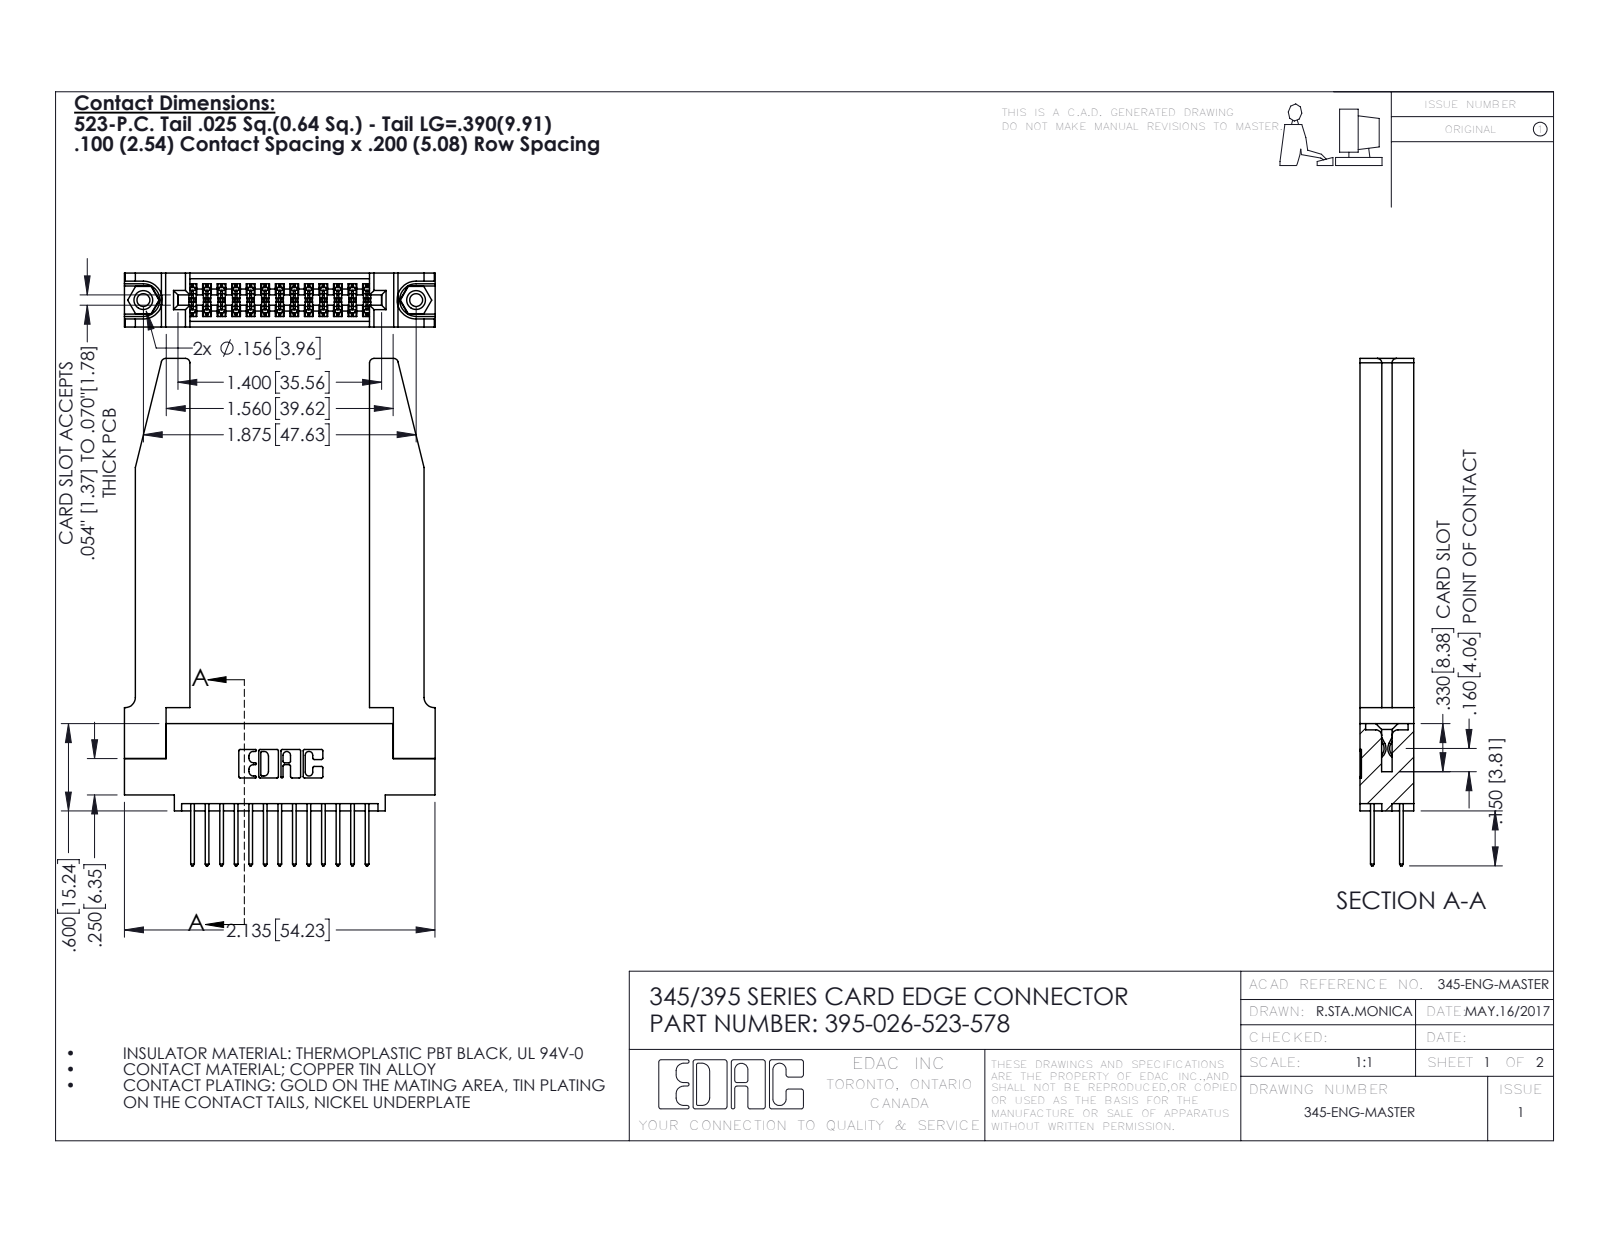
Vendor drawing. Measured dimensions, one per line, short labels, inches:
name: 395-026-523-578; 345 Part_0.110 Offset - 0.156 Dia-TH; 345-220-078_345-220-078; 345-250-001_345-250-001-102 (+1 more)
written by: SolidWorks 2016 (CONFIG_CONTROL_DESIGN)
unit: in
bodies: 31 solids, 1664 faces (1084 planar, 528 cylindrical, 52 other)
size: 3.487 × 2.136 × 0.37
volume: 0.778 in³; area: 21.66 in²
holes: 2× ⌀0.089, 2× ⌀0.125, 2× ⌀0.156, 1× ⌀0.064
bosses: 2× ⌀0.155
rounds: 39× R0.006, 26× R0.01, 22× R0.01, 8× R0.03, 6× R0.007, 6× R0.031, 3× R0.026, 2× R0.014
face distances: 0.37, 0.072, 0.298, 0.2, 0.098, 0.272, 0.025, 0.148, 0.15, 0.22
hole spacings: 0.27, 1.643, 1.875
